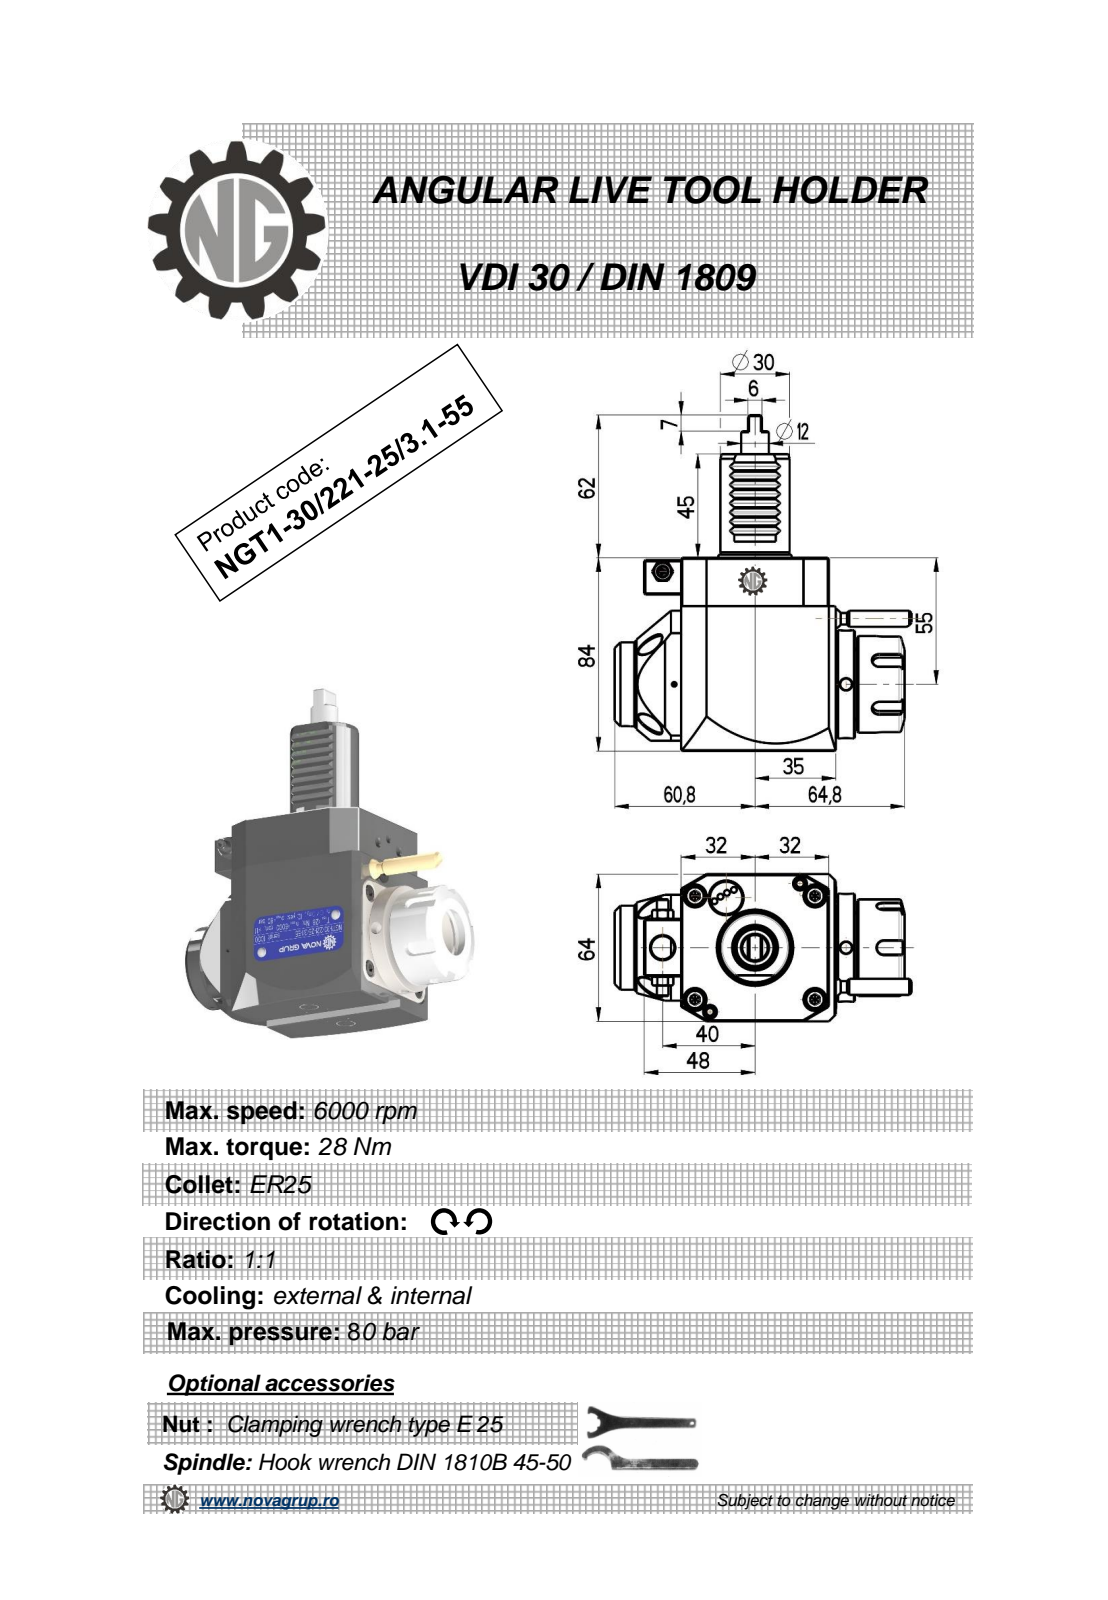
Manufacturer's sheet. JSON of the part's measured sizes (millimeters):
{"part_name": "NGT1_30_221_25_3_1_55", "step_written_by": "PRO/ENGINEER BY PARAMETRIC TECHNOLOGY CORPORATION, 2010280 (CONFIG_CONTROL_DESIGN)", "units": "millimeters", "bodies": {"solids": 1, "faces": 414, "planar": 186, "cylindrical": 82, "other": 146}, "overall_size": [146, 128.63, 64], "volume_mm3": 469978, "surface_area_mm2": 47703, "round_holes": [[5, 2], [2.5, 1], [3, 1], [4.2, 1], [9.5, 1], [10, 1], [20.3, 1]], "round_bosses_or_shafts": [[8.96, 2], [5, 2], [47, 1], [42, 1], [36.5, 1], [35, 1], [30, 1], [12, 1]], "partial_cylinders_radius": [[0.26, 12], [0.3, 8], [3, 5], [0.8, 2], [160, 2], [32, 1]], "face_to_face_distances": [64, 84, 0.5, 67.2, 67, 3, 3.2, 7.5, 80, 8], "hole_center_spacings": [24.76, 33.19, 46.5, 79.45, 93.35]}
